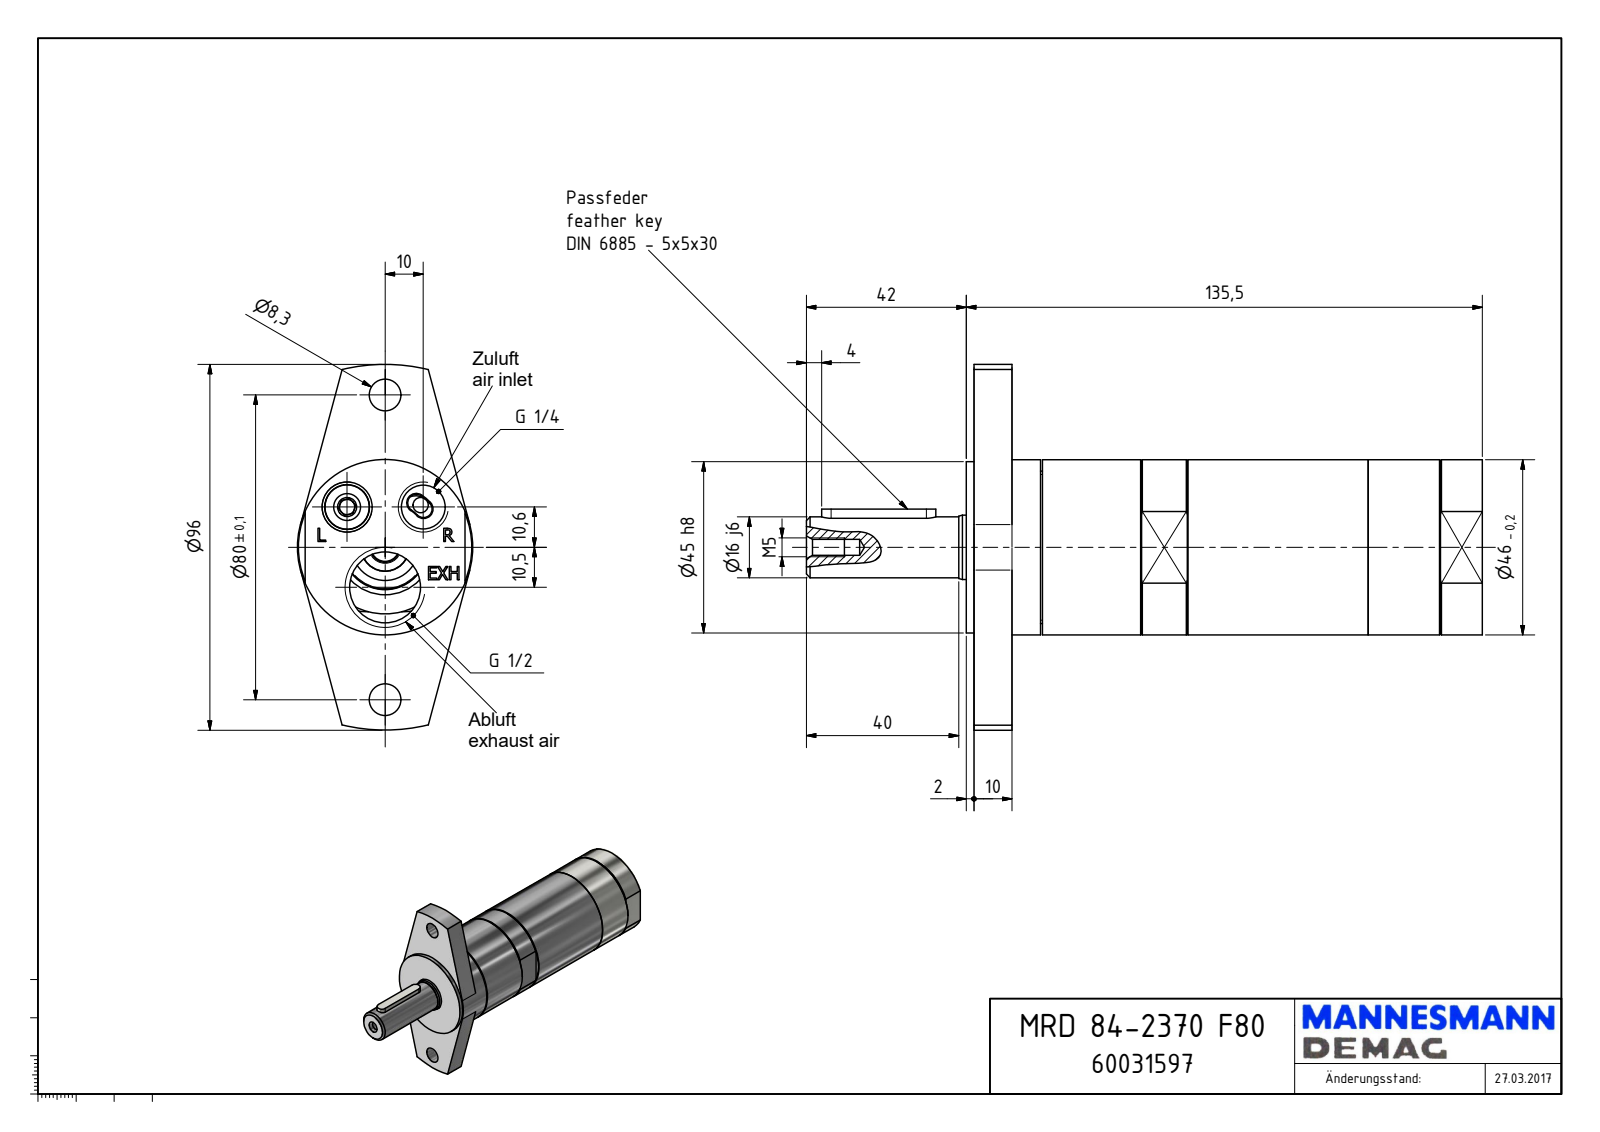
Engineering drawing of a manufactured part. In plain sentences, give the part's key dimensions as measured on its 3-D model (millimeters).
The part is named "MRD 84-2370 F80_60031597". Its 3-D file was written by "Autodesk Inventor 2018 (AUTOMOTIVE_DESIGN)". It is 1 solid with 165 faces: 108 planar, 31 cylindrical and 26 other. Overall it measures 177.5 by 96 by 46 millimeters. Its volume is 243 806 cubic millimeters and its surface area 32 690 square millimeters. Round holes: 2 of diameter 8.3, 1 of diameter 4, 1 of diameter 4.13, 1 of diameter 11.45, 1 of diameter 17.5, 1 of diameter 18.63. Round bosses or shafts: 1 of diameter 46, 1 of diameter 45, 1 of diameter 40, 1 of diameter 33.93, 1 of diameter 16.95, 1 of diameter 16. Partial cylindrical surfaces (rounded edges, fillets, slot ends): 2 of radius 2.5, 2 of radius 5, 1 of radius 5.72, 1 of radius 19, 1 of radius 48. The main face-to-face distances are 10, 12, 2, 123.5, 135.5, 133.5, 42, 8, 115.5, 46. The hole center spacings are 14.57, 23.35, 31.05, 40, 51.58, 10.5, 20, 29.5.
